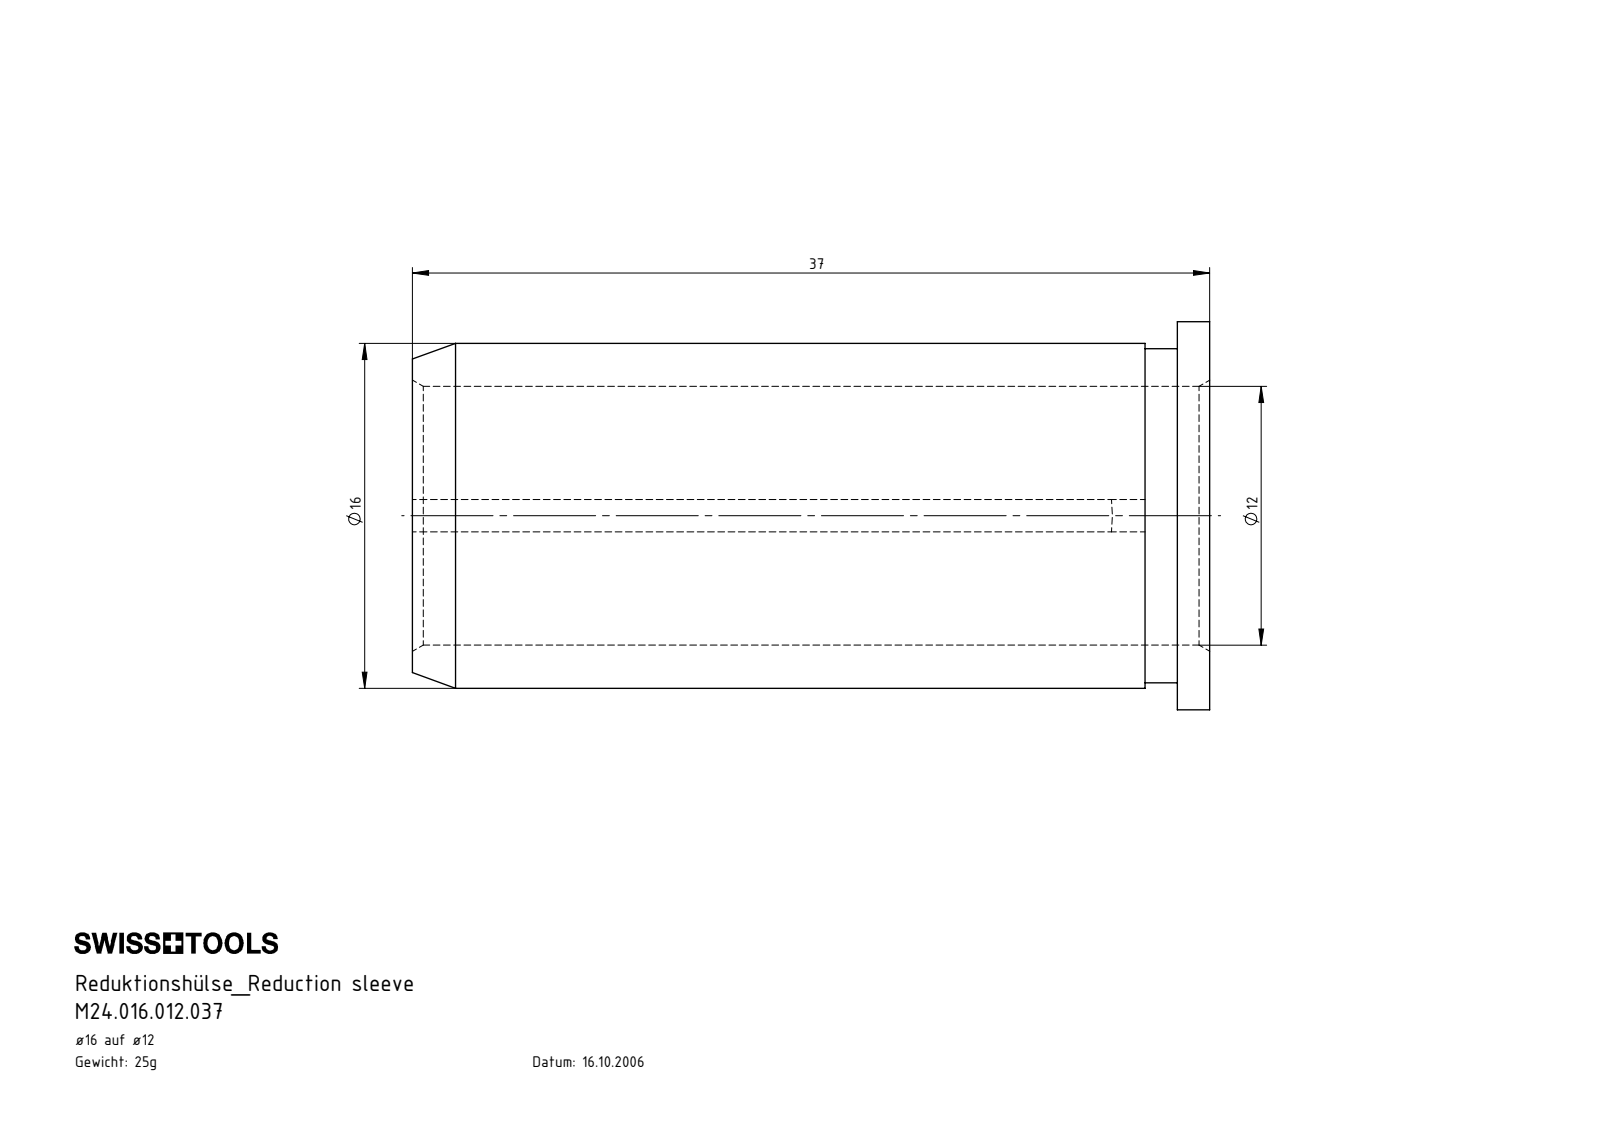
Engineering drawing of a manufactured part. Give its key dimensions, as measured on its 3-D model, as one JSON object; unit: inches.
{"part_name": "U12.U16.001.037", "step_written_by": "SolidWorks 2017 (AUTOMOTIVE_DESIGN)", "units": "inches", "bodies": {"solids": 1, "faces": 14, "planar": 6, "cylindrical": 5, "other": 3}, "overall_size": [1.457, 0.709, 0.709], "volume_in3": 0.194, "surface_area_in2": 5.51, "round_holes": [[0.472, 1]], "round_bosses_or_shafts": [[0.709, 1], [0.63, 1], [0.61, 1]], "partial_cylinders_radius": [[1.24, 1]], "face_to_face_distances": [0.059, 1.398, 1.457, 1.339, 0.118]}
